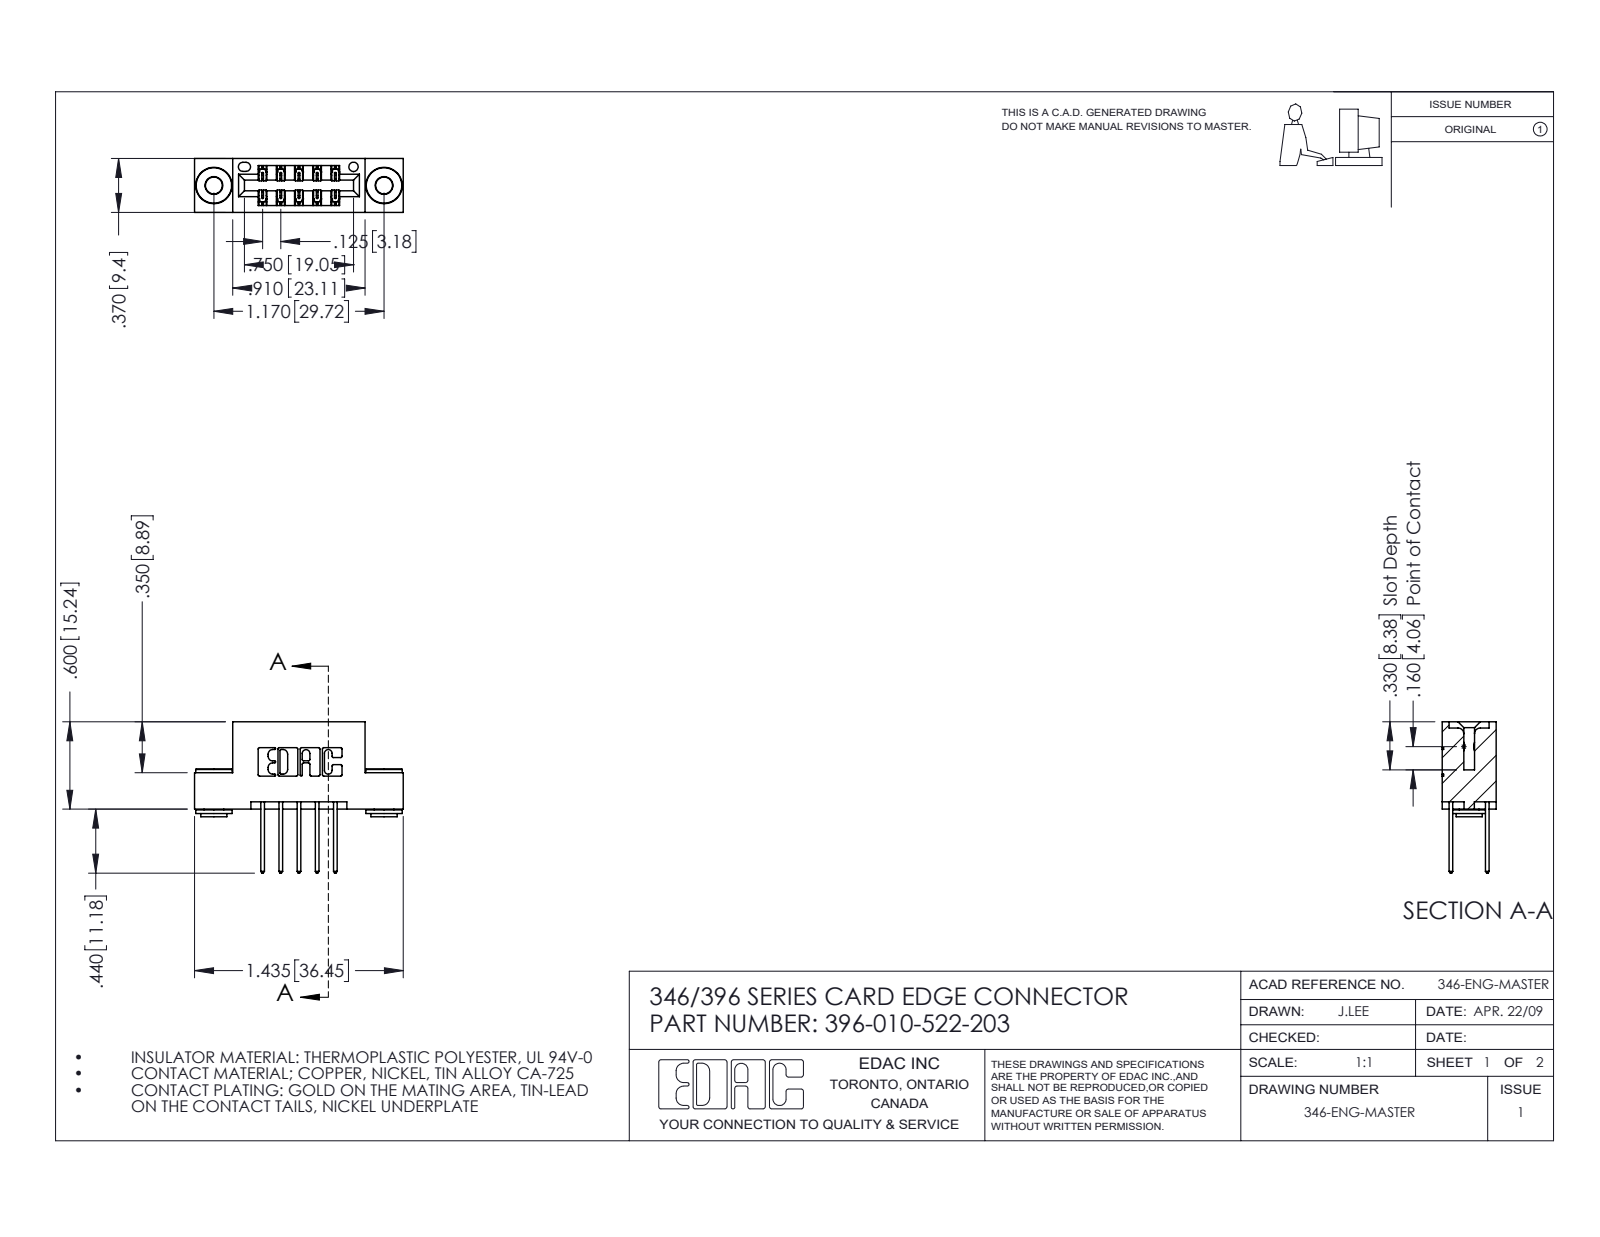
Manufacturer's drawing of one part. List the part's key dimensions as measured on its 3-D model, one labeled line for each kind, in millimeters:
Part name (STEP PRODUCT): 346 Part_Flush Mounting Lugs - 0.156 Dia-TH; 345-250-002_345-250-002-102; 345-292-001_345-293-122; 396-010-522-203
STEP written by: SolidWorks 2016 (CONFIG_CONTROL_DESIGN)
Units: millimetres
Bodies: 13 solids, 680 faces (436 planar, 236 cylindrical, 8 other)
Overall size (bounding box): 36.4 × 26.4 × 9.4
Volume: 3 310 mm³ · Surface area: 4 304 mm²
Round holes (diameter × count): ⌀2.9 ×2, ⌀4 ×2, ⌀1.6 ×1
Round bosses / shafts (diameter × count): ⌀6.4 ×2, ⌀4.6 ×2, ⌀3.5 ×2
Partial cylindrical surfaces — rounded edges, fillets, slot ends (radius × count): R0.3 ×22, R0.2 ×15, R0.3 ×10, R0.2 ×6, R0.8 ×6, R0.7 ×3, R0.4 ×2, R0.6 ×2
Main face-to-face distances: 6.4, 1.2, 8.2, 9.4, 0.6, 1.8, 7.6, 7, 3.8, 5.6
Hole centre spacings: 6.2, 24.6, 29.7
